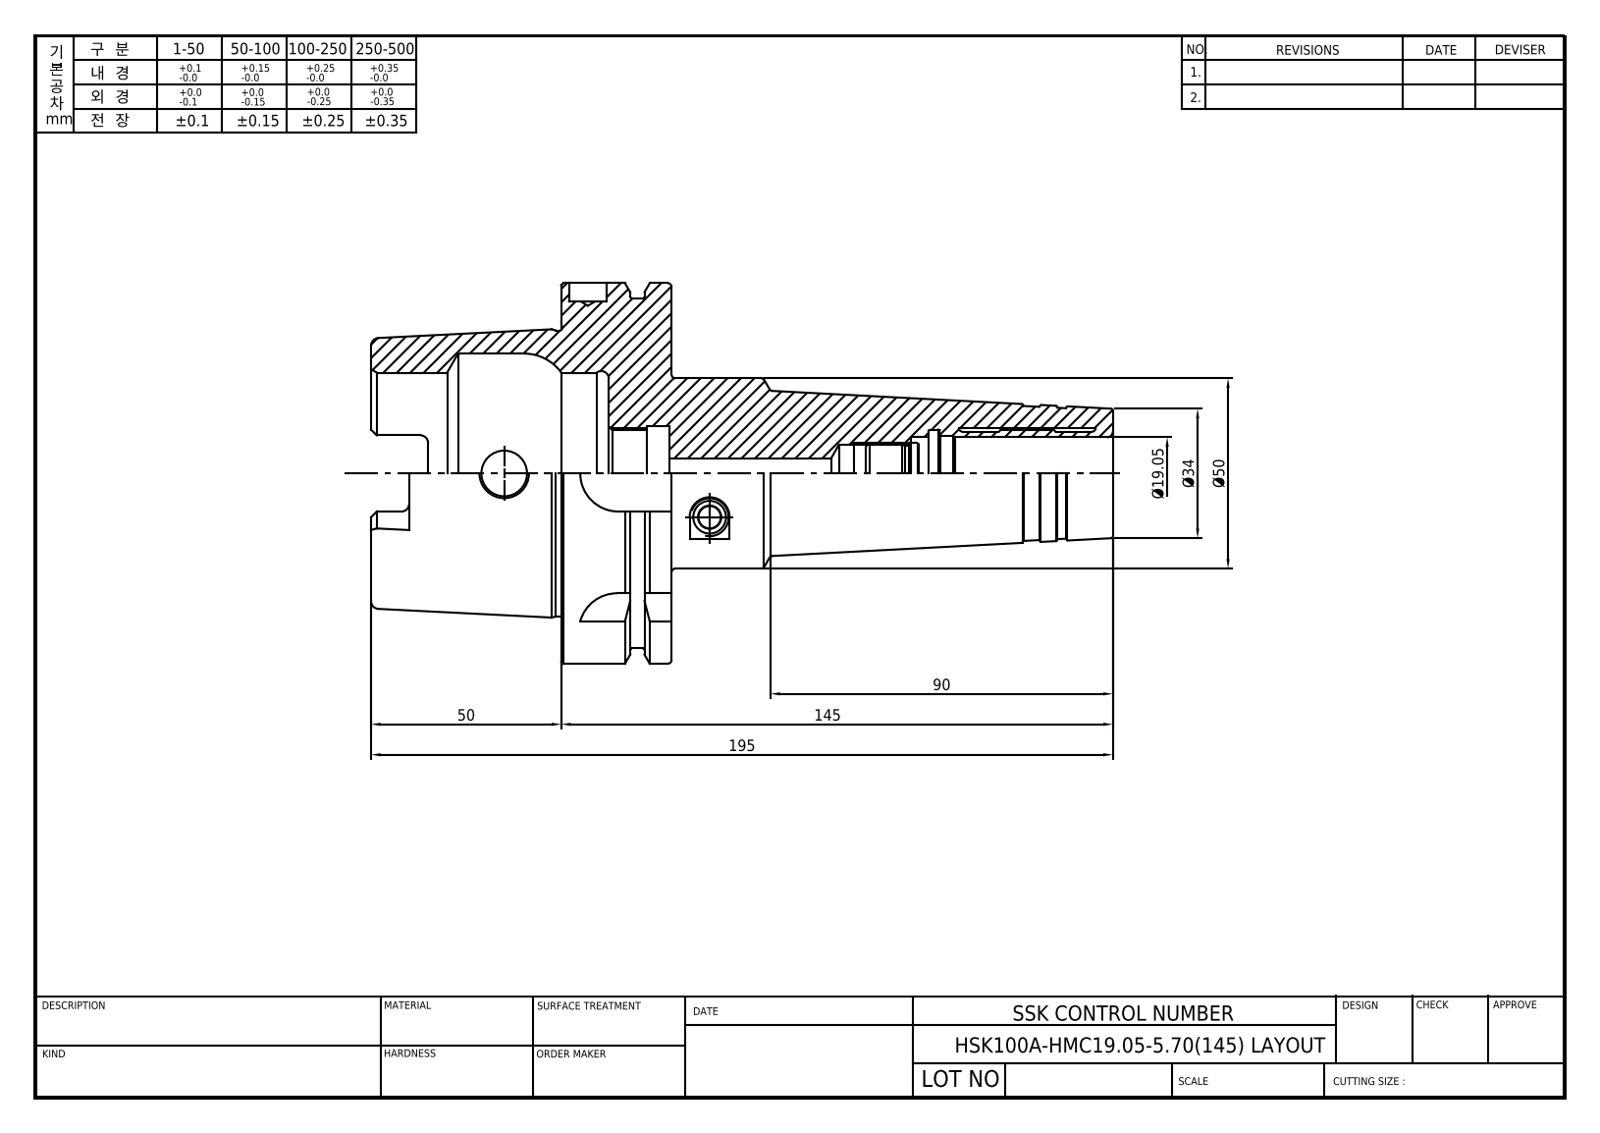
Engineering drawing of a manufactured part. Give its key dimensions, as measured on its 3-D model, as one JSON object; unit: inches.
{"part_name": "LO_HSK100A-HMC3_4-5_71-WR110HMC", "step_written_by": "CREO PARAMETRIC BY PTC INC, 2018100 (CONFIG_CONTROL_DESIGN)", "units": "inches", "bodies": {"solids": 1, "faces": 206, "planar": 50, "cylindrical": 52, "other": 104}, "overall_size": [7.677, 3.937, 3.937], "volume_in3": 23.6, "surface_area_in2": 109.2, "round_holes": [[0.331, 1], [0.394, 1], [0.472, 1], [0.594, 1], [0.75, 1], [0.768, 1], [0.886, 1], [0.945, 1], [0.984, 1], [2.087, 1], [2.518, 1]], "round_bosses_or_shafts": [[3.937, 1], [3.622, 1], [2.959, 1], [1.969, 1]], "partial_cylinders_radius": [[0.079, 6], [0.192, 4], [0.394, 4]], "face_to_face_distances": [1.142, 0.492, 0.65, 2.461, 1.969, 3.11, 0.394, 2.854, 0.886, 0.256]}
